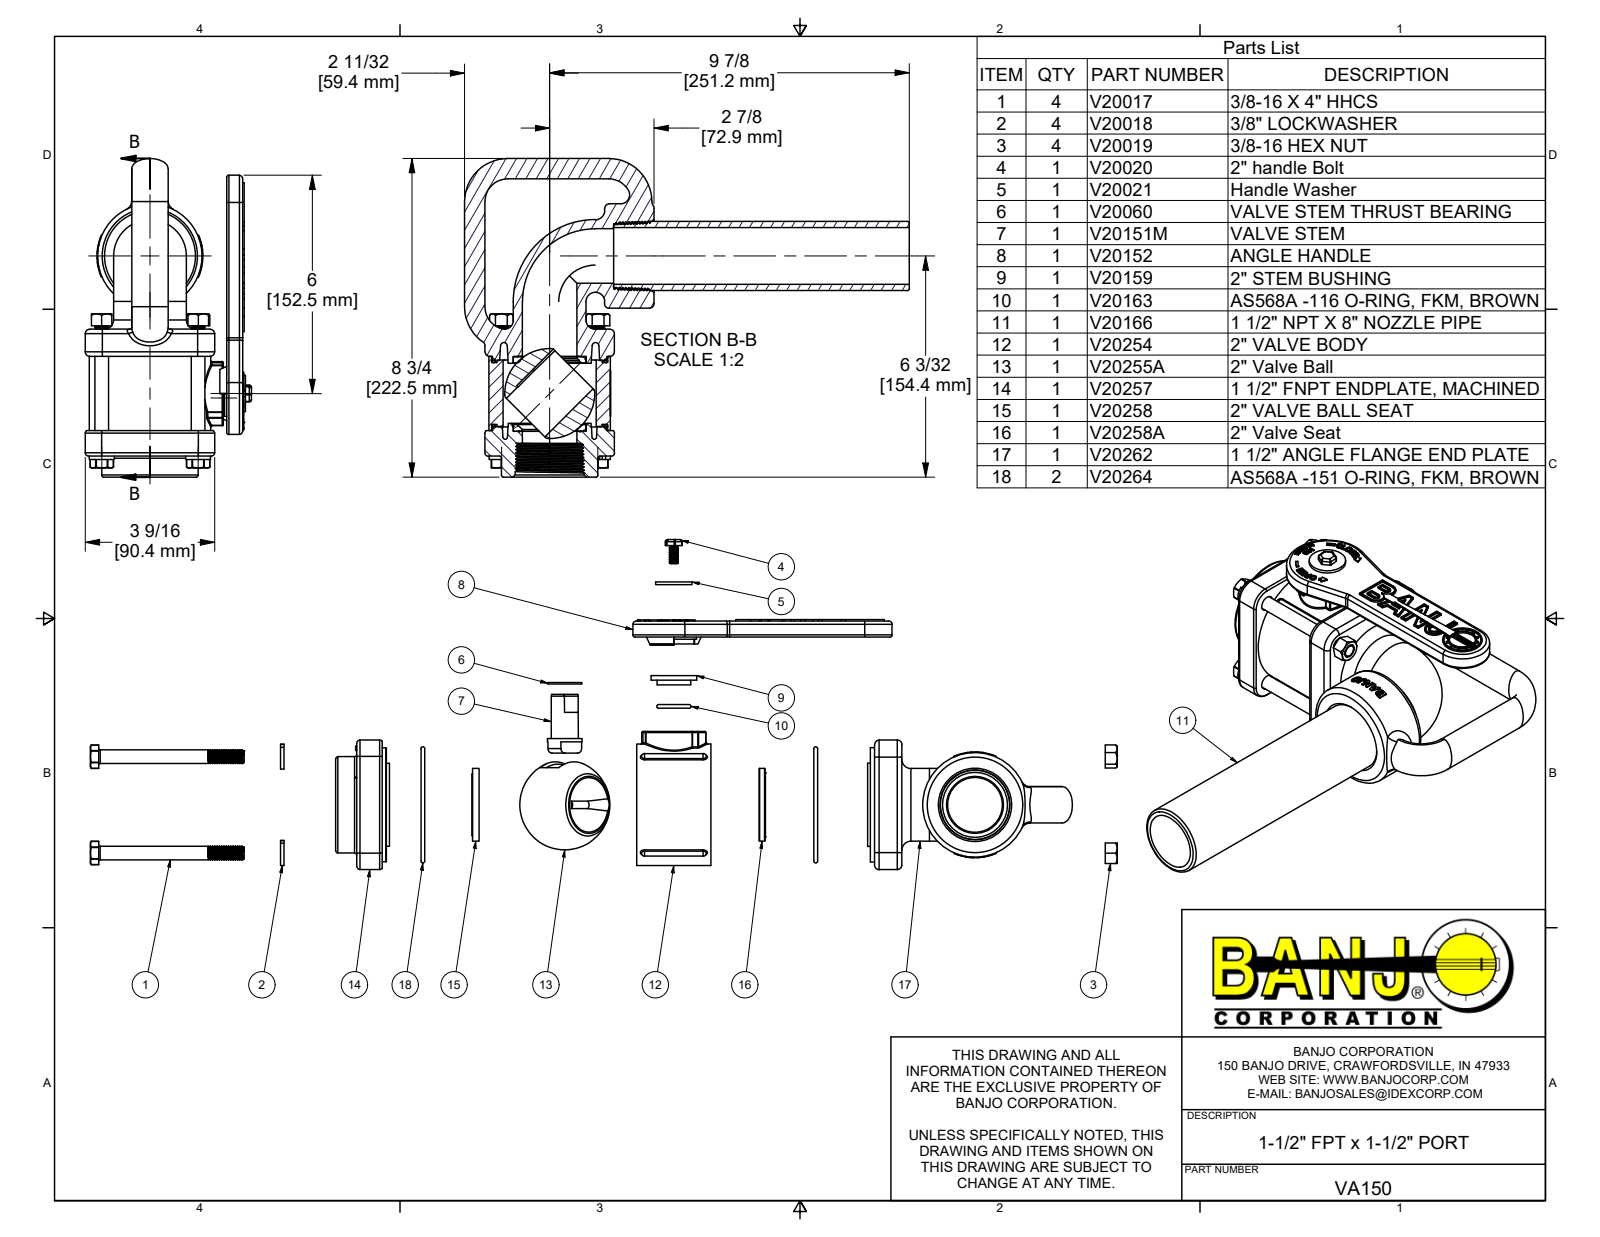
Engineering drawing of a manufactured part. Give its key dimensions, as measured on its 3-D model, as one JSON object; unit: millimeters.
{"part_name": "VA150; V20254; V20257; VX20257 (+8 more)", "step_written_by": "Autodesk Inventor 2022 (CONFIG_CONTROL_DESIGN)", "units": "millimeters", "bodies": {"solids": 30, "faces": 2080, "planar": 791, "cylindrical": 513, "other": 776}, "overall_size": [310.6, 222.5, 116.1], "volume_mm3": 909300, "surface_area_mm2": 295500, "round_holes": [[4.2, 10], [9.5, 5], [7.8, 4], [9.8, 4], [10.3, 4], [10.7, 4], [38.1, 3], [5, 1], [7.1, 1], [8.9, 1], [18.4, 1], [19.1, 1]], "round_bosses_or_shafts": [[8.2, 60], [17.4, 4], [9.5, 4], [50.8, 2], [79.9, 1], [79.5, 1], [73.4, 1], [72.9, 1]], "partial_cylinders_radius": [[0.8, 38], [2.3, 22], [3.2, 17], [1.5, 12], [4.1, 8], [0.4, 4], [2.4, 4], [8.1, 4]], "face_to_face_distances": [19.1, 17.8, 90.4, 6.2, 88.6, 69.6, 51.8, 70.9, 2.9, 48.9], "hole_center_spacings": [34.6, 58.8, 59, 66.9, 67.4, 17.9, 24.7, 24.8]}
